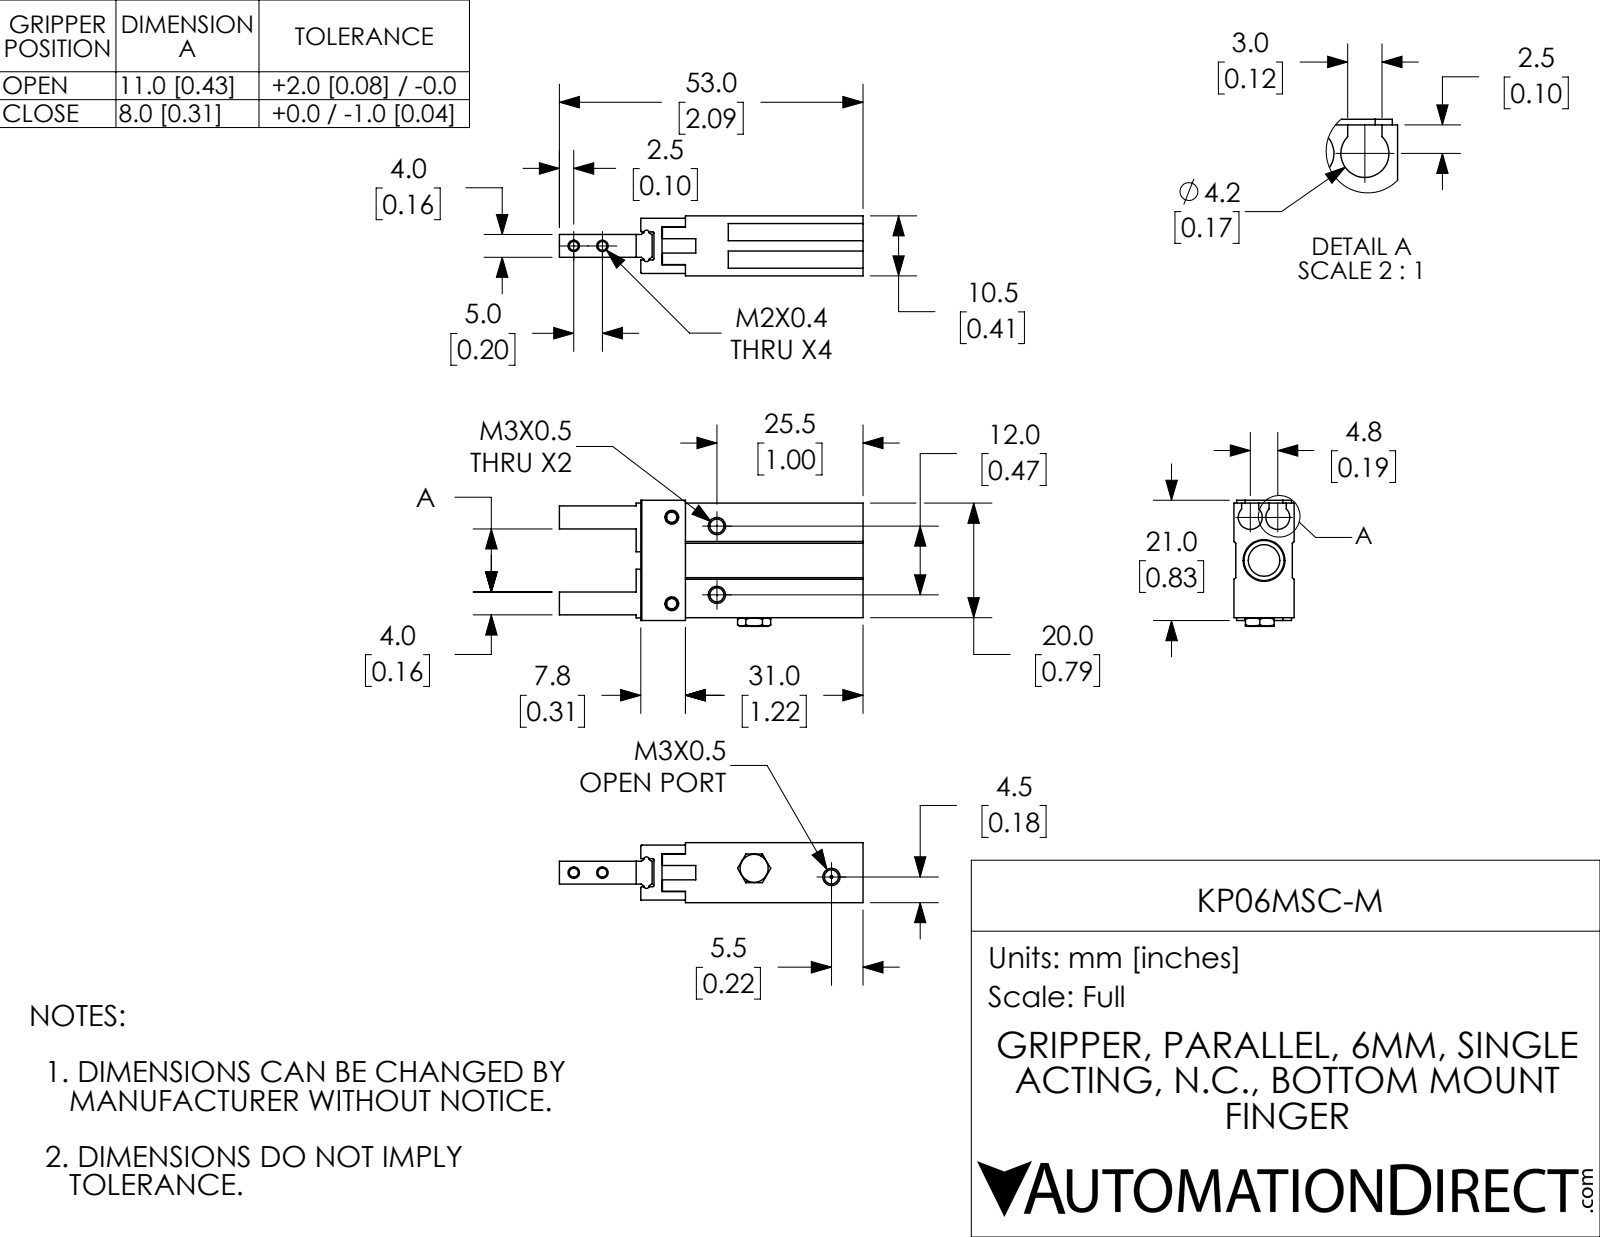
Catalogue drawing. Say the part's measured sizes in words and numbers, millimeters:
The part is named "KP06MSC-M; KP06MSC-M-3; KP06MSC-M-2; KP06MSC-M-1". Its 3-D file was written by "SolidWorks 2017 (CONFIG_CONTROL_DESIGN)". It is 3 solids with 196 faces: 102 planar, 44 cylindrical and 50 other. Overall it measures 53 by 22 by 10.5 millimeters. Its volume is 7 054 cubic millimeters and its surface area 5 221 square millimeters. Round holes: 3 of diameter 2.46, 2 of diameter 0.5, 2 of diameter 1.57, 2 of diameter 3.1, 1 of diameter 2.46, 1 of diameter 5.5, 1 of diameter 7. Partial cylindrical surfaces (rounded edges, fillets, slot ends): 4 of radius 0.2, 2 of radius 0.5, 2 of radius 2.1. The main face-to-face distances are 3.25, 10.5, 2, 4, 10.2, 3.7, 0.45, 2.8, 6.5, 10.05. The hole center spacings are 5, 12, 13.58, 26.51, 31.51, 40.01, 45.01.
